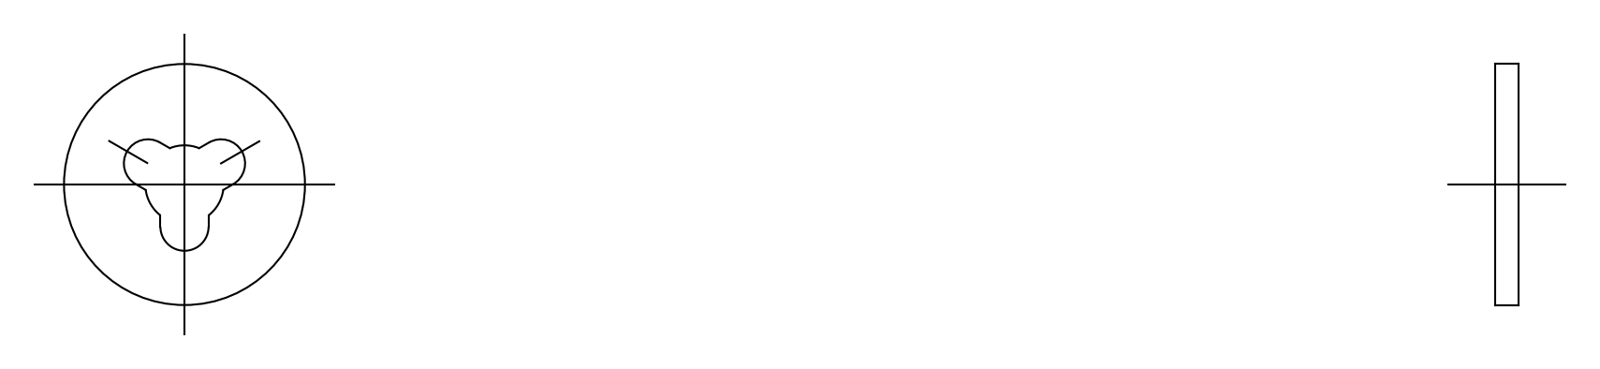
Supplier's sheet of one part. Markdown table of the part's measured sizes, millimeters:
| quantity | value |
| --- | --- |
| STEP written by | spGate 19.8.4 (****-****-****-****) (AUTOMOTIVE_DESIGN) |
| units | millimeters |
| bodies | 1 solid, 16 faces (8 planar, 8 cylindrical, 0 other) |
| overall size | 8 × 8 × 0.8 |
| volume | 33 mm³ |
| surface area | 112 mm² |
| round bosses / shafts (diameter × count) | 8 × 1 |
| partial cylindrical surfaces (radius × count) | 0.8 × 3, 1.3 × 1 |
| main face-to-face distances | 0.8, 1.6 |
